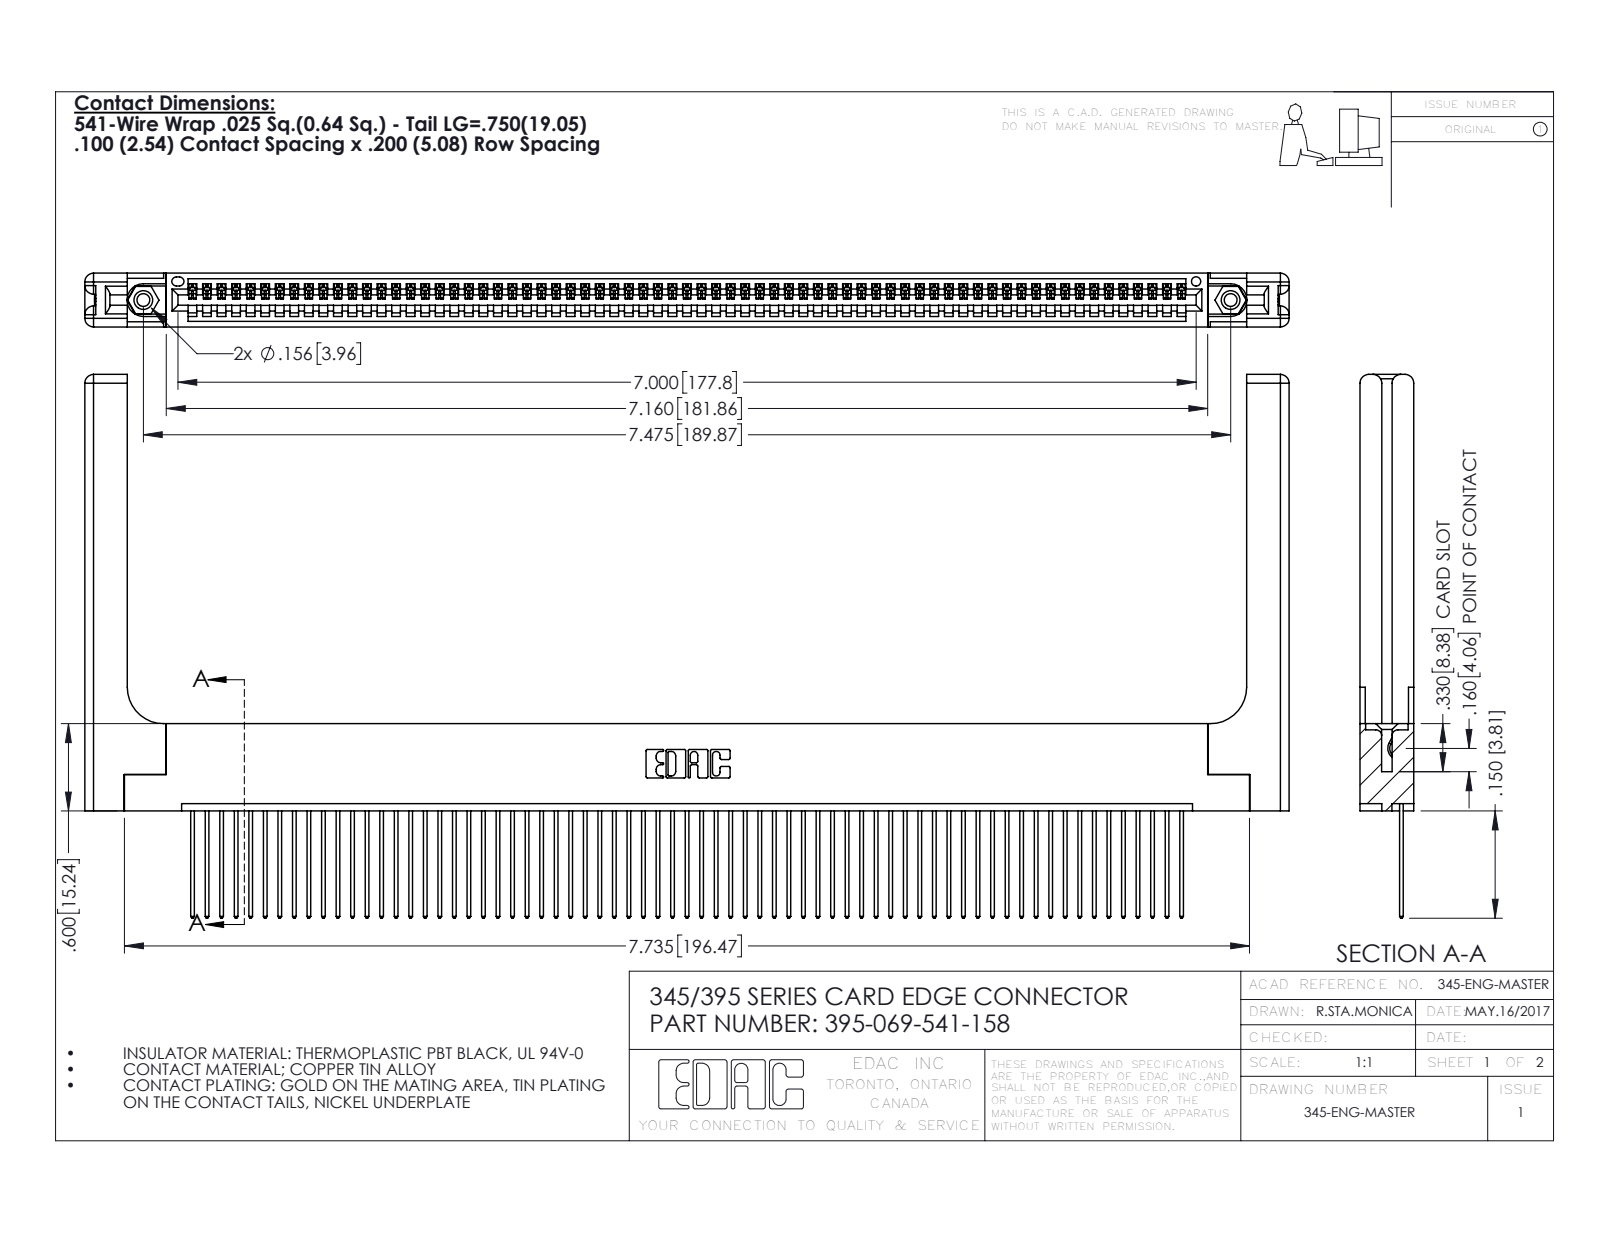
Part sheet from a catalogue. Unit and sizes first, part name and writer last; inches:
Units: inches
Overall size (bounding box): 8.279 × 3.737 × 0.37
Round holes (diameter × count): ⌀0.089 ×2, ⌀0.125 ×2, ⌀0.156 ×2, ⌀0.064 ×1
Round bosses / shafts (diameter × count): ⌀0.155 ×2
Partial cylindrical surfaces — rounded edges, fillets, slot ends (radius × count): R0.006 ×138, R0.01 ×138, R0.01 ×22, R0.06 ×16, R0.007 ×6, R0.031 ×6, R0.026 ×3, R0.03 ×2
Main face-to-face distances: 0.072, 0.298, 0.37, 0.098, 0.272, 0.025, 0.2, 0.225, 0.148, 0.15
Hole centre spacings: 0.27, 7.239, 7.475
Volume: 1.765 in³ · Surface area: 52.93 in²
Bodies: 74 solids, 4384 faces (2988 planar, 1336 cylindrical, 60 other)
Part name (STEP PRODUCT): 395-069-541-158; 345 Part_Flush Mounting Lugs - 0.156 Dia-TH; 345-250-001_345-250-001-102; 345-292-001_345-293-141 (+1 more)
STEP written by: SolidWorks 2016 (CONFIG_CONTROL_DESIGN)
